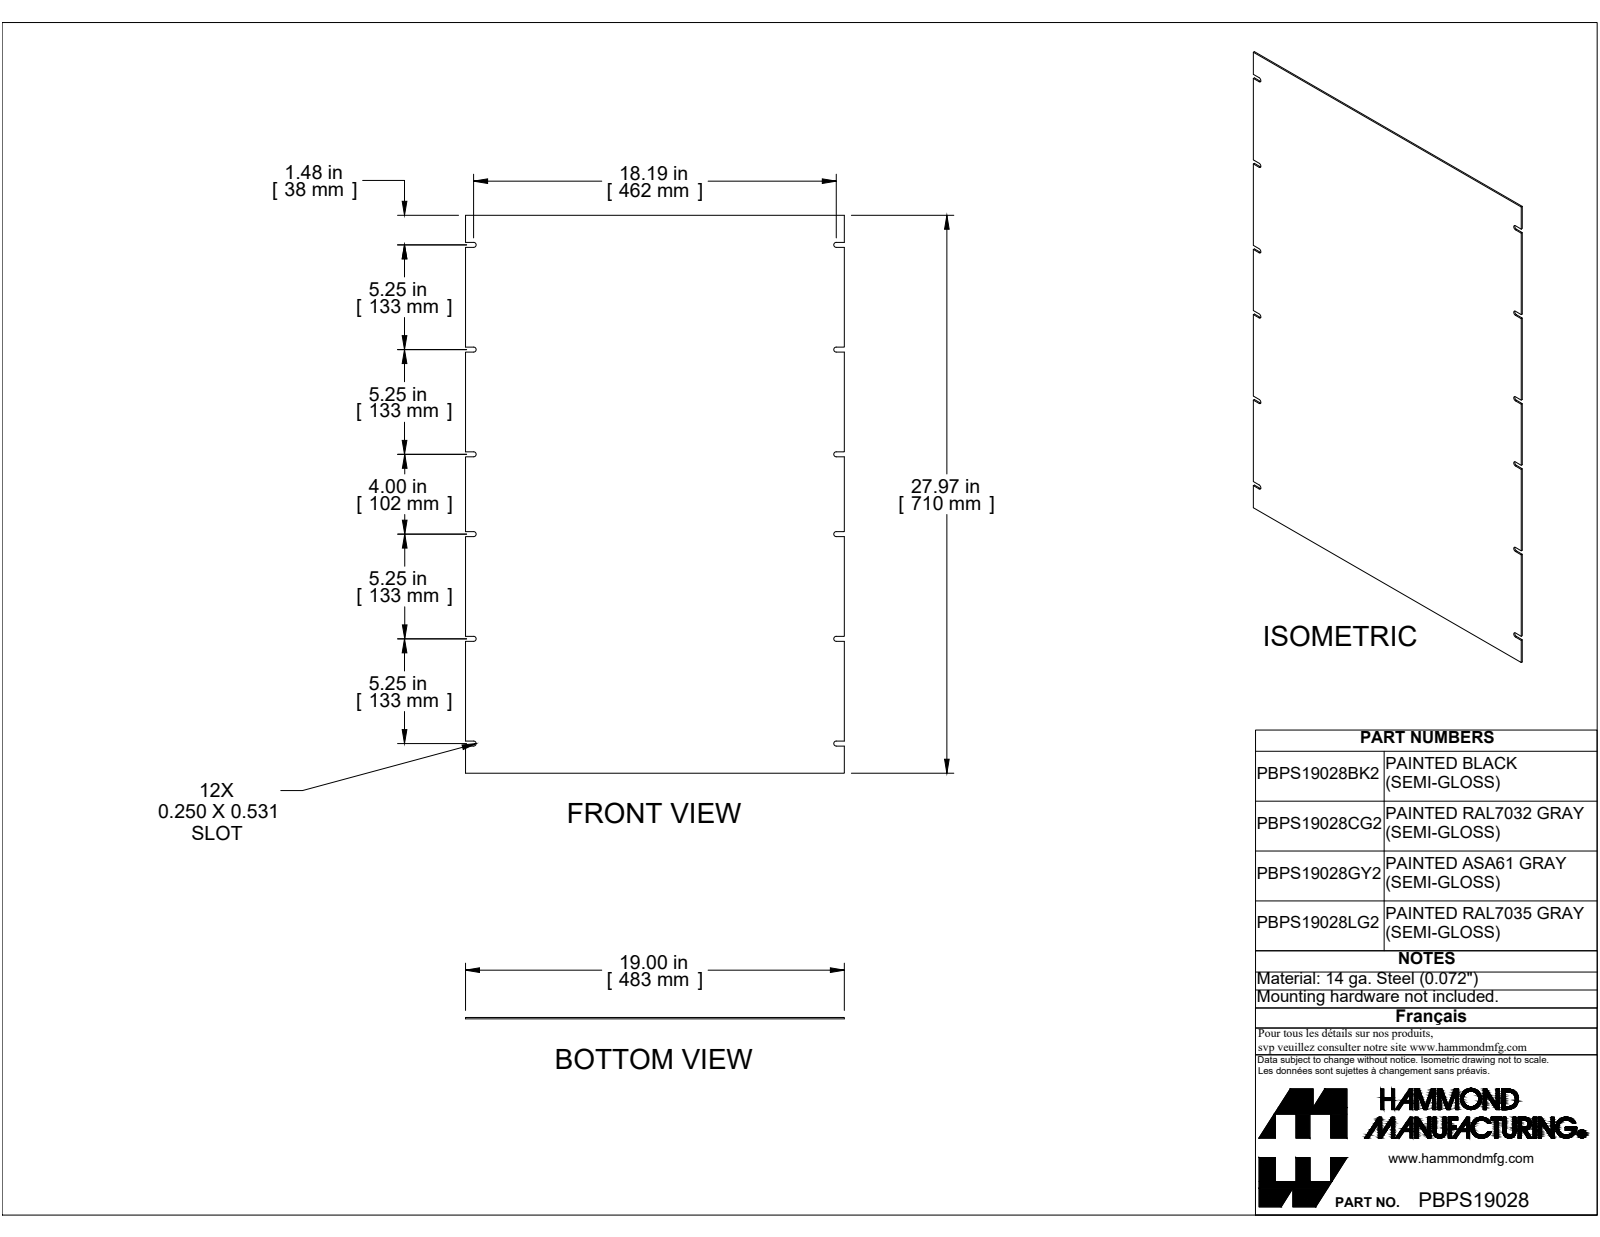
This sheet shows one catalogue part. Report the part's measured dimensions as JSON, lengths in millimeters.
{"part_name": "PBPS19028GY2", "step_written_by": "SolidWorks 2019 (CONFIG_CONTROL_DESIGN)", "units": "millimeters", "bodies": {"solids": 1, "faces": 54, "planar": 42, "cylindrical": 12, "other": 0}, "overall_size": [710.4, 482.6, 1.8], "volume_mm3": 625200, "surface_area_mm2": 688400, "partial_cylinders_radius": [[3.2, 12]], "face_to_face_distances": [1.8, 482.6, 710.4, 133.4, 368.3, 6.4, 139.7, 133.4, 127, 6.4]}
